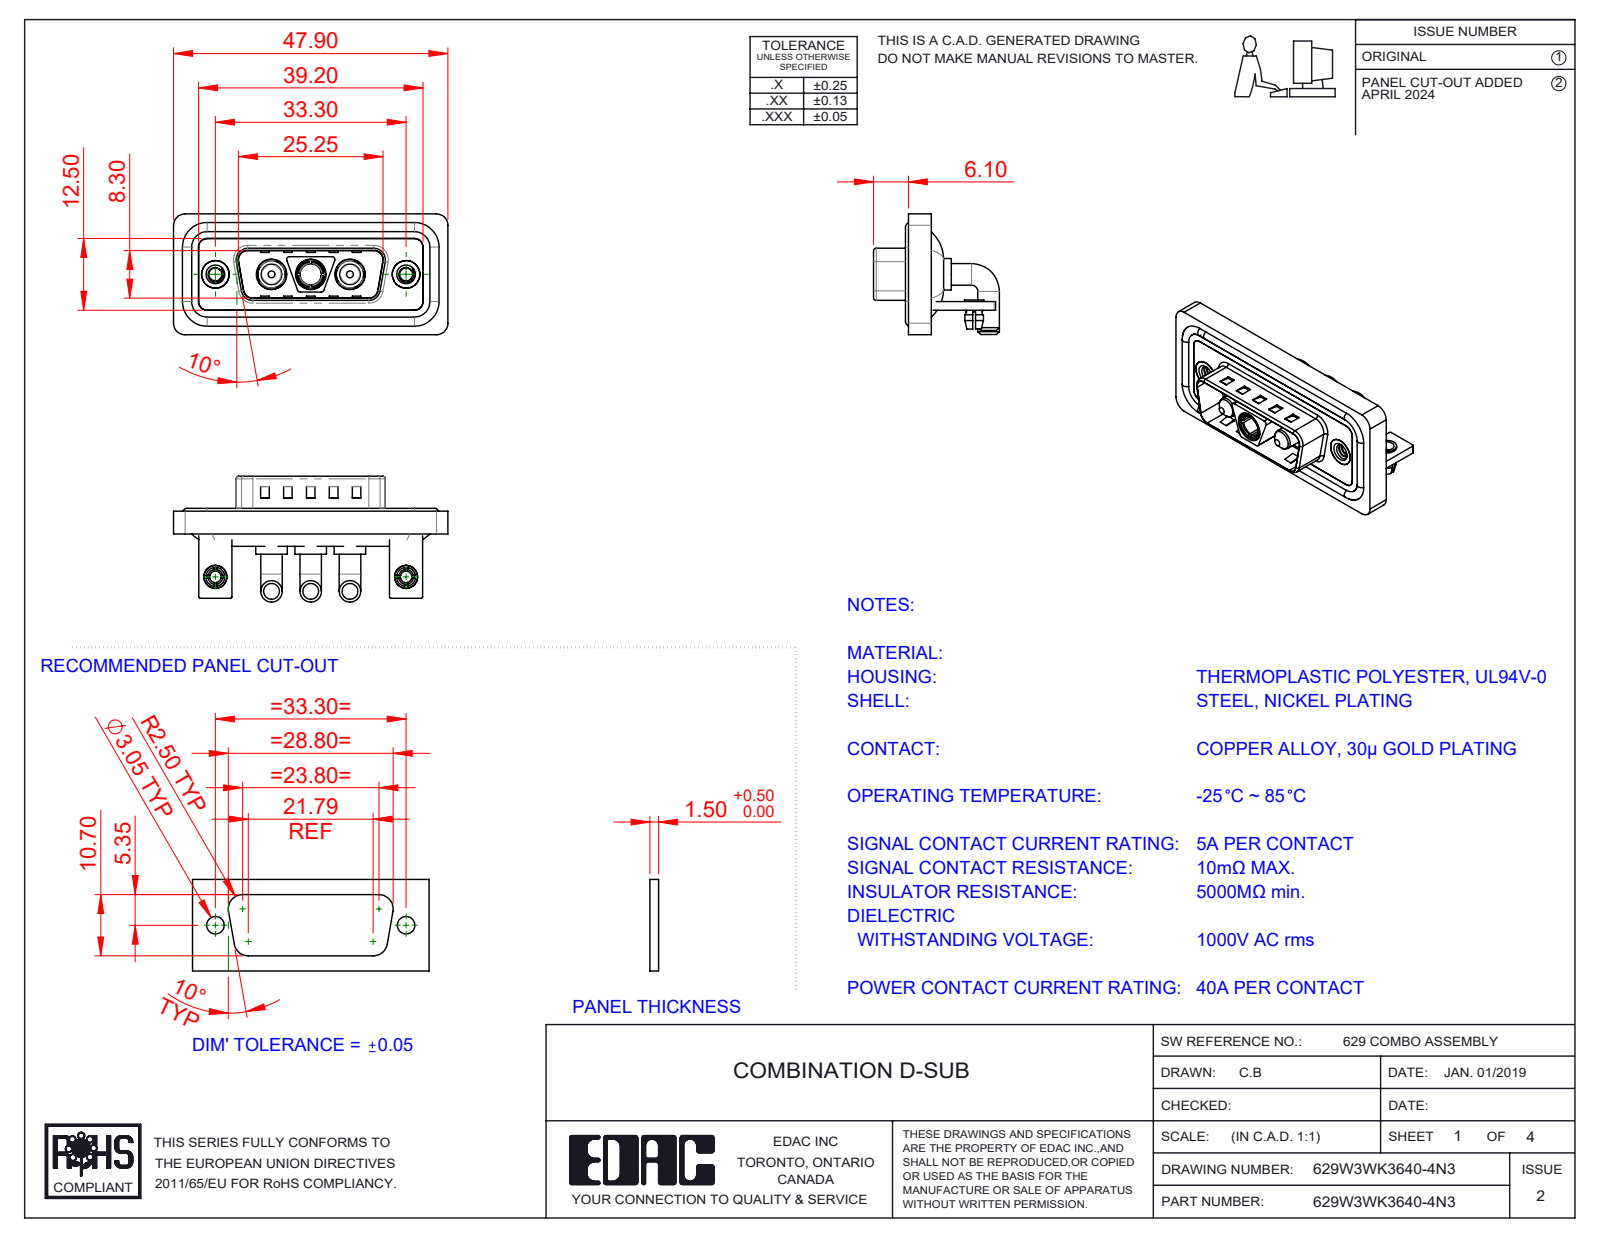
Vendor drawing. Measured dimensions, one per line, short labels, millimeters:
name: 629Combo Housing_3WK3; 629W3WK3640-4N3; 629Combo Shell Front_15 Contacts; 629Combo Board Lock (+6 more)
written by: SolidWorks 2023 (CONFIG_CONTROL_DESIGN)
unit: mm
bodies: 17 solids, 753 faces (299 planar, 306 cylindrical, 148 other)
size: 47.9 × 21.98 × 21.1
volume: 6 421 mm³; area: 10 347 mm²
holes: 3× ⌀4.85, 3× ⌀5.3, 2× ⌀2, 2× ⌀2.26, 2× ⌀2.5, 2× ⌀3.2, 2× ⌀4, 2× ⌀4.8, 2× ⌀5, 1× ⌀3.7
bosses: 6× ⌀3.75, 4× ⌀1.6, 3× ⌀5.5, 3× ⌀5.2, 3× ⌀4.75, 2× ⌀4.9, 2× ⌀4, 2× ⌀3.6
rounds: 21× R2, 18× R1.5, 16× R0.25, 13× R0.5, 8× R1.6, 4× R0.6, 4× R0.65, 4× R0.9
face distances: 0.4, 1.5, 0.8, 2.9, 1.1, 2.1, 3.7, 1.6, 1.2, 4.5
hole spacings: 6.85, 9.8, 16.65, 23.5, 33.3, 13.7
